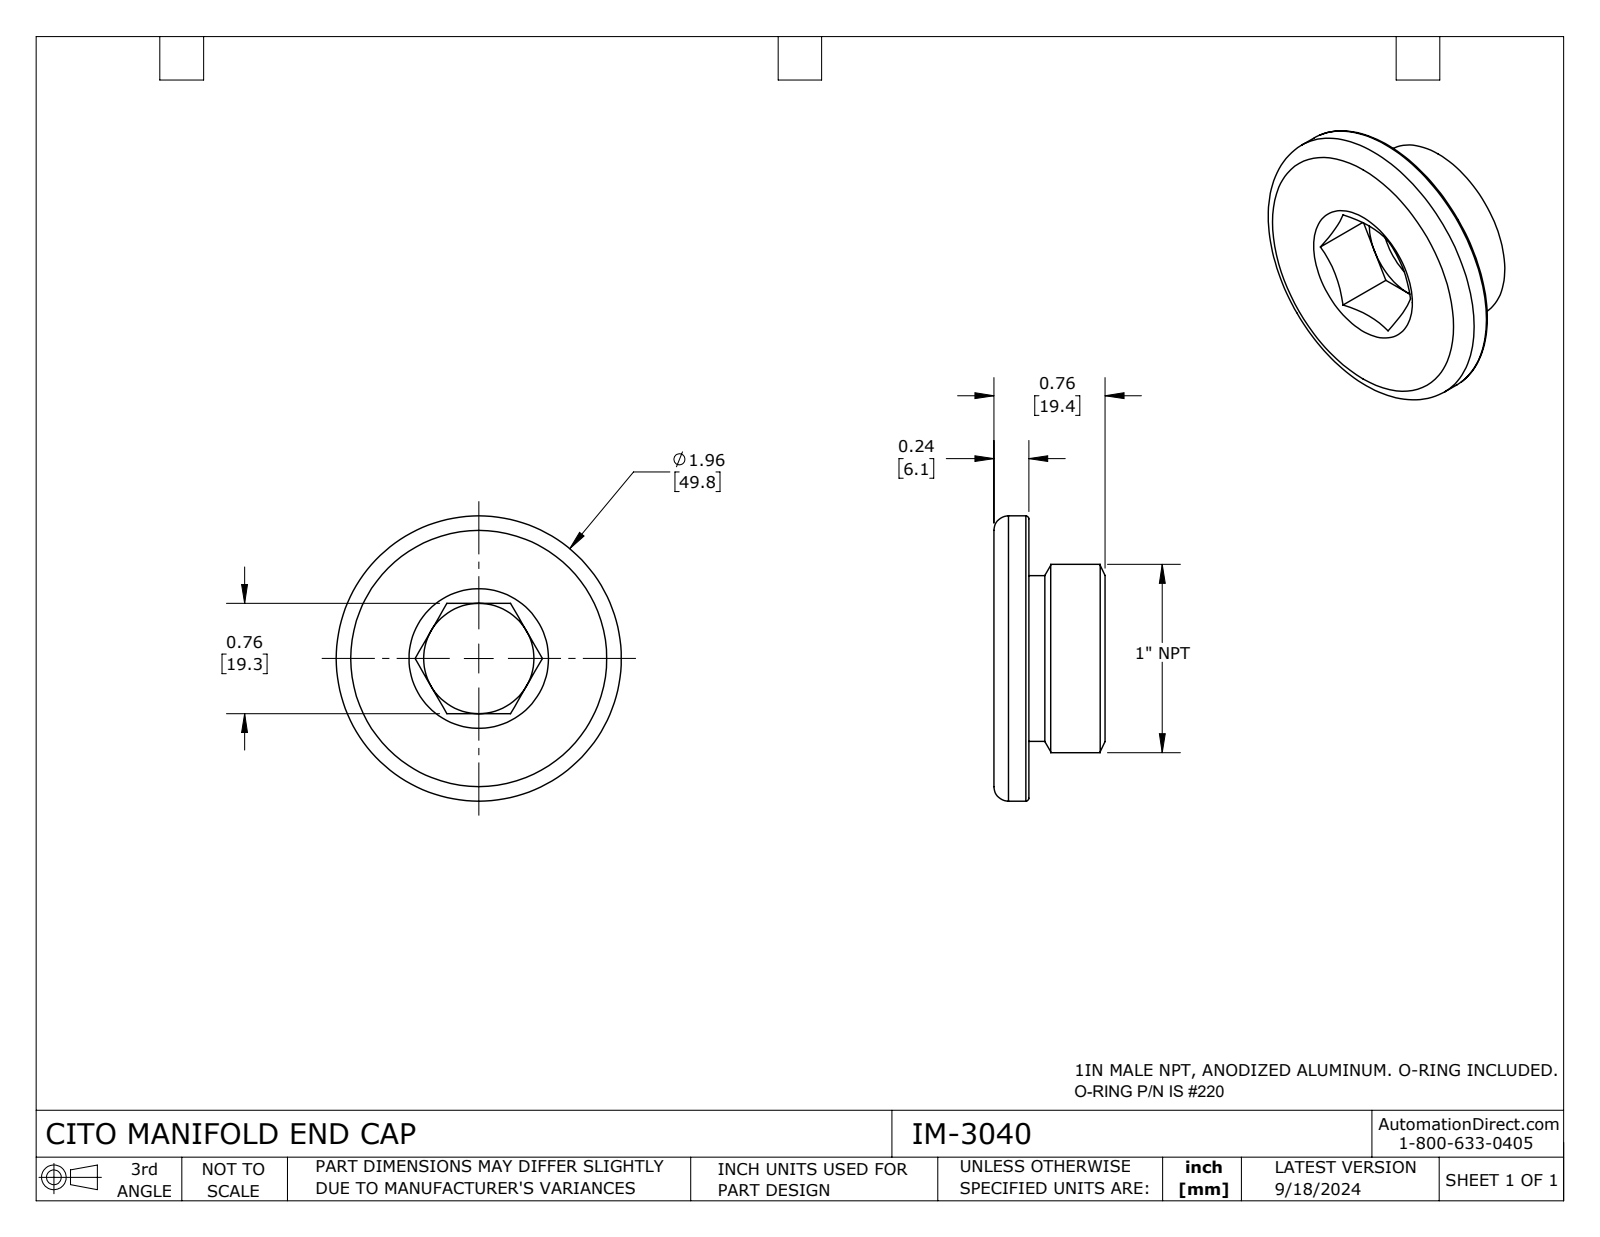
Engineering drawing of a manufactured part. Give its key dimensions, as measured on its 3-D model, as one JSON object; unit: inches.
{"part_name": "IM-3040", "step_written_by": "SolidWorks 2023 (CONFIG_CONTROL_DESIGN)", "units": "inches", "bodies": {"solids": 1, "faces": 51, "planar": 21, "cylindrical": 12, "other": 18}, "overall_size": [1.96, 1.96, 0.764], "volume_in3": 1, "surface_area_in2": 11.91, "round_holes": [[0.758, 1], [1.637, 1]], "round_bosses_or_shafts": [[1.96, 1], [1.359, 1], [1.293, 1], [1.14, 1]], "face_to_face_distances": [0.24, 0.764, 0.524, 0.758, 0.2, 0.324, 0.125, 0.115, 0.639, 0.564]}
